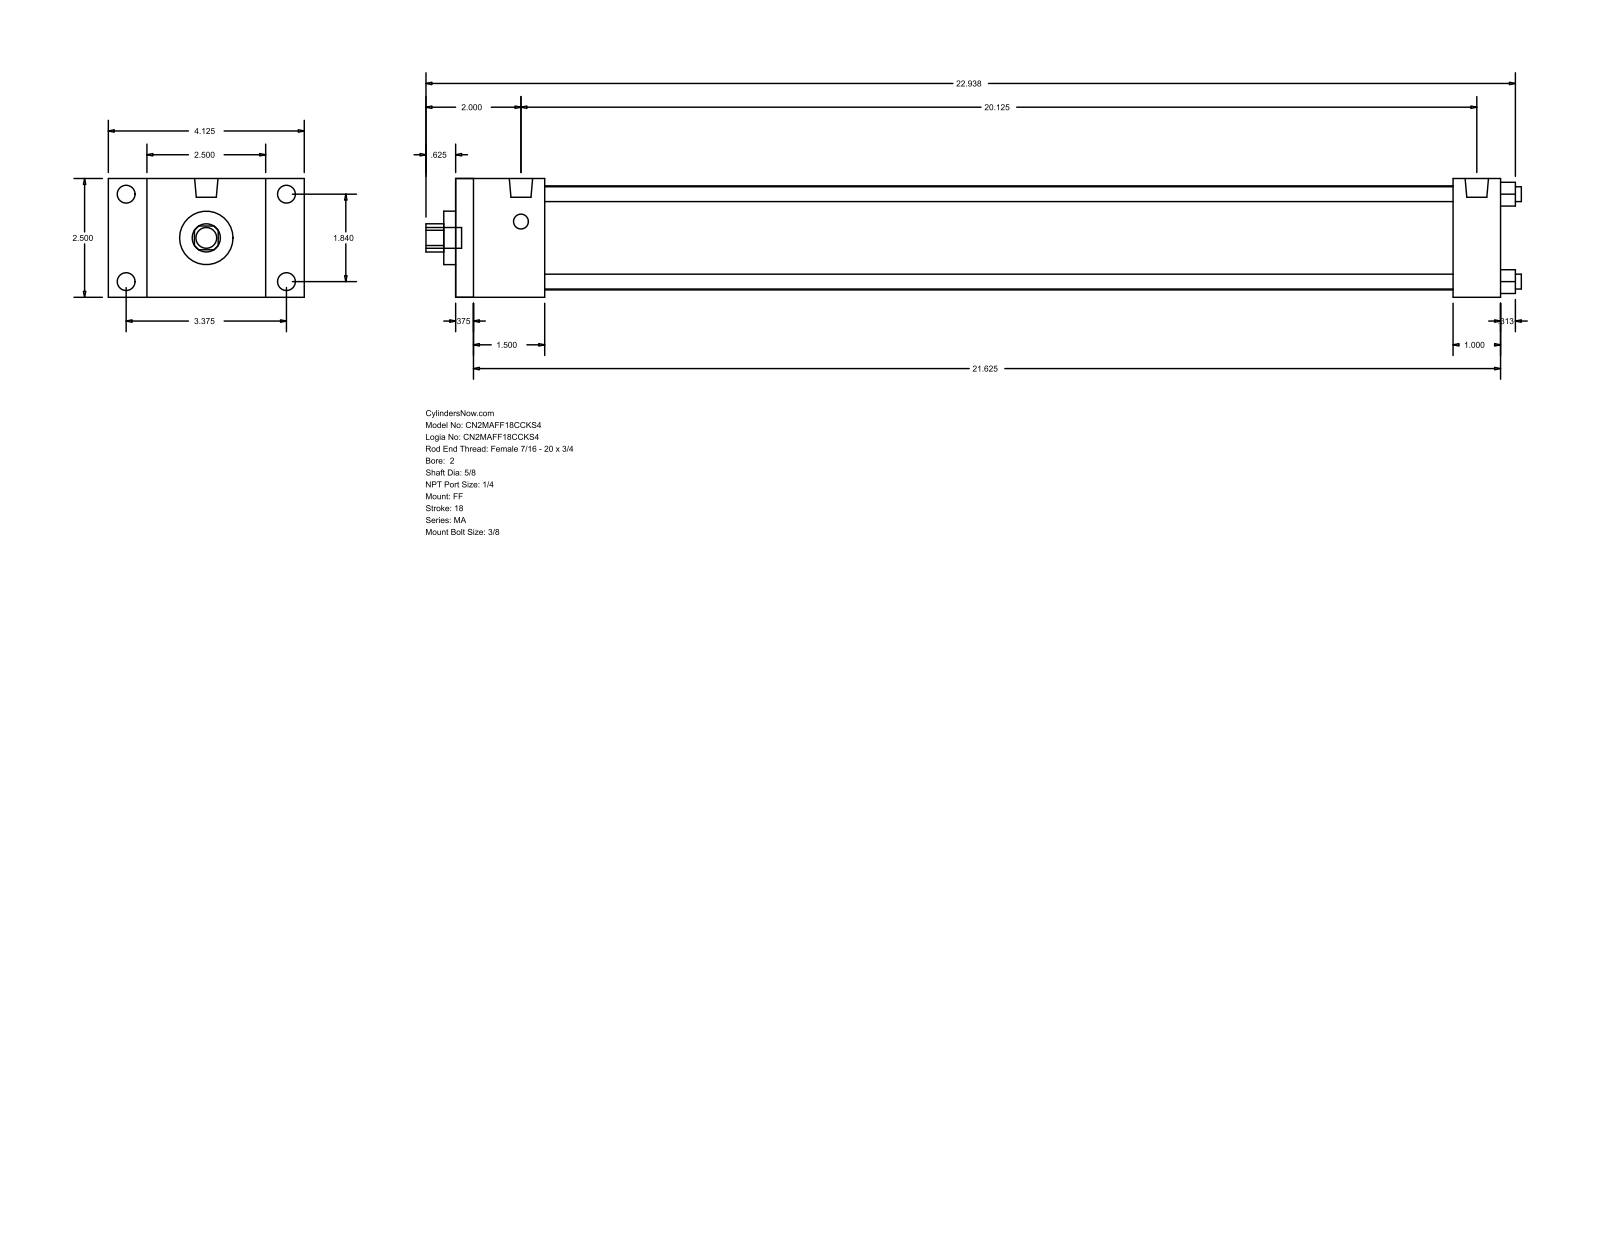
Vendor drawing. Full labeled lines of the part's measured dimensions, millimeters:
Part name (STEP PRODUCT): MA_FF__0200_0.625
STEP written by: GSSL Pune (CONFIG_CONTROL_DESIGN)
Units: millimetres
Bodies: 0 solids, 92 faces (64 planar, 28 cylindrical, 0 other)
Overall size (bounding box): 585.79 × 104.78 × 63.5
Round holes (diameter × count): ⌀7.94 ×4, ⌀15.88 ×1, ⌀28.57 ×1, ⌀55.63 ×1
Round bosses / shafts (diameter × count): ⌀9.53 ×4, ⌀7.94 ×4, ⌀12.49 ×2, ⌀11.11 ×1
Partial cylindrical surfaces — rounded edges, fillets, slot ends (radius × count): R7.54 ×1
Main face-to-face distances: 63.5, 558.79, 9.52, 549.27, 25.4, 38.1, 47.62, 533.39, 523.87, 485.77
Hole centre spacings: 33.05, 46.74, 66.1
